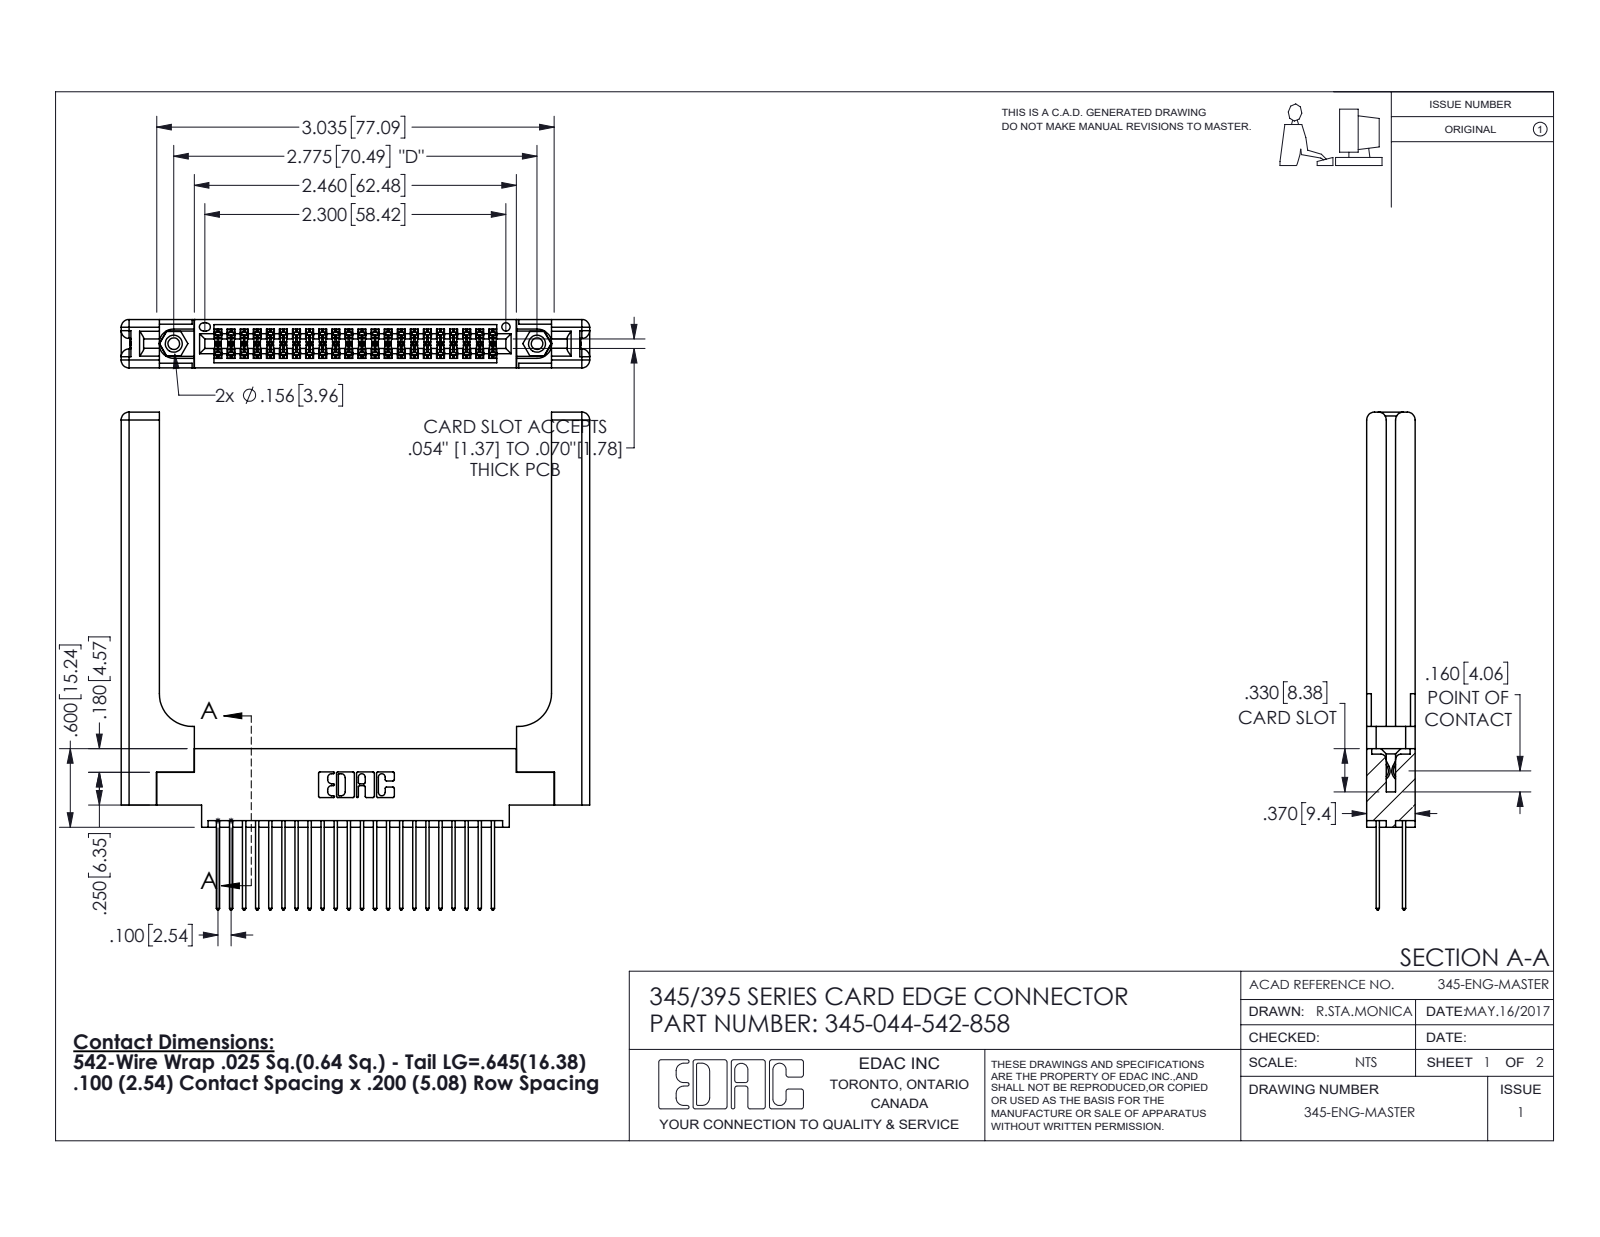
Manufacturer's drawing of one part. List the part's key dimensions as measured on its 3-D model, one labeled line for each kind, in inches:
Part name (STEP PRODUCT): 345-292-001_345-293-142; 345-250-001_345-250-001-102; 345-044-542-858; 345-220-058_345-220-058 (+1 more)
STEP written by: SolidWorks 2016 (CONFIG_CONTROL_DESIGN)
Units: inches
Bodies: 49 solids, 2586 faces (1684 planar, 842 cylindrical, 60 other)
Overall size (bounding box): 3.802 × 3.579 × 0.37
Volume: 1.05 in³ · Surface area: 28.97 in²
Round holes (diameter × count): ⌀0.089 ×2, ⌀0.125 ×2, ⌀0.156 ×2, ⌀0.064 ×1
Round bosses / shafts (diameter × count): ⌀0.155 ×2
Partial cylindrical surfaces — rounded edges, fillets, slot ends (radius × count): R0.006 ×66, R0.01 ×44, R0.01 ×22, R0.06 ×16, R0.007 ×6, R0.031 ×6, R0.026 ×3, R0.014 ×2
Main face-to-face distances: 0.37, 0.072, 0.298, 0.098, 0.272, 0.025, 0.2, 0.225, 0.15, 0.148
Hole centre spacings: 0.27, 2.541, 2.775
